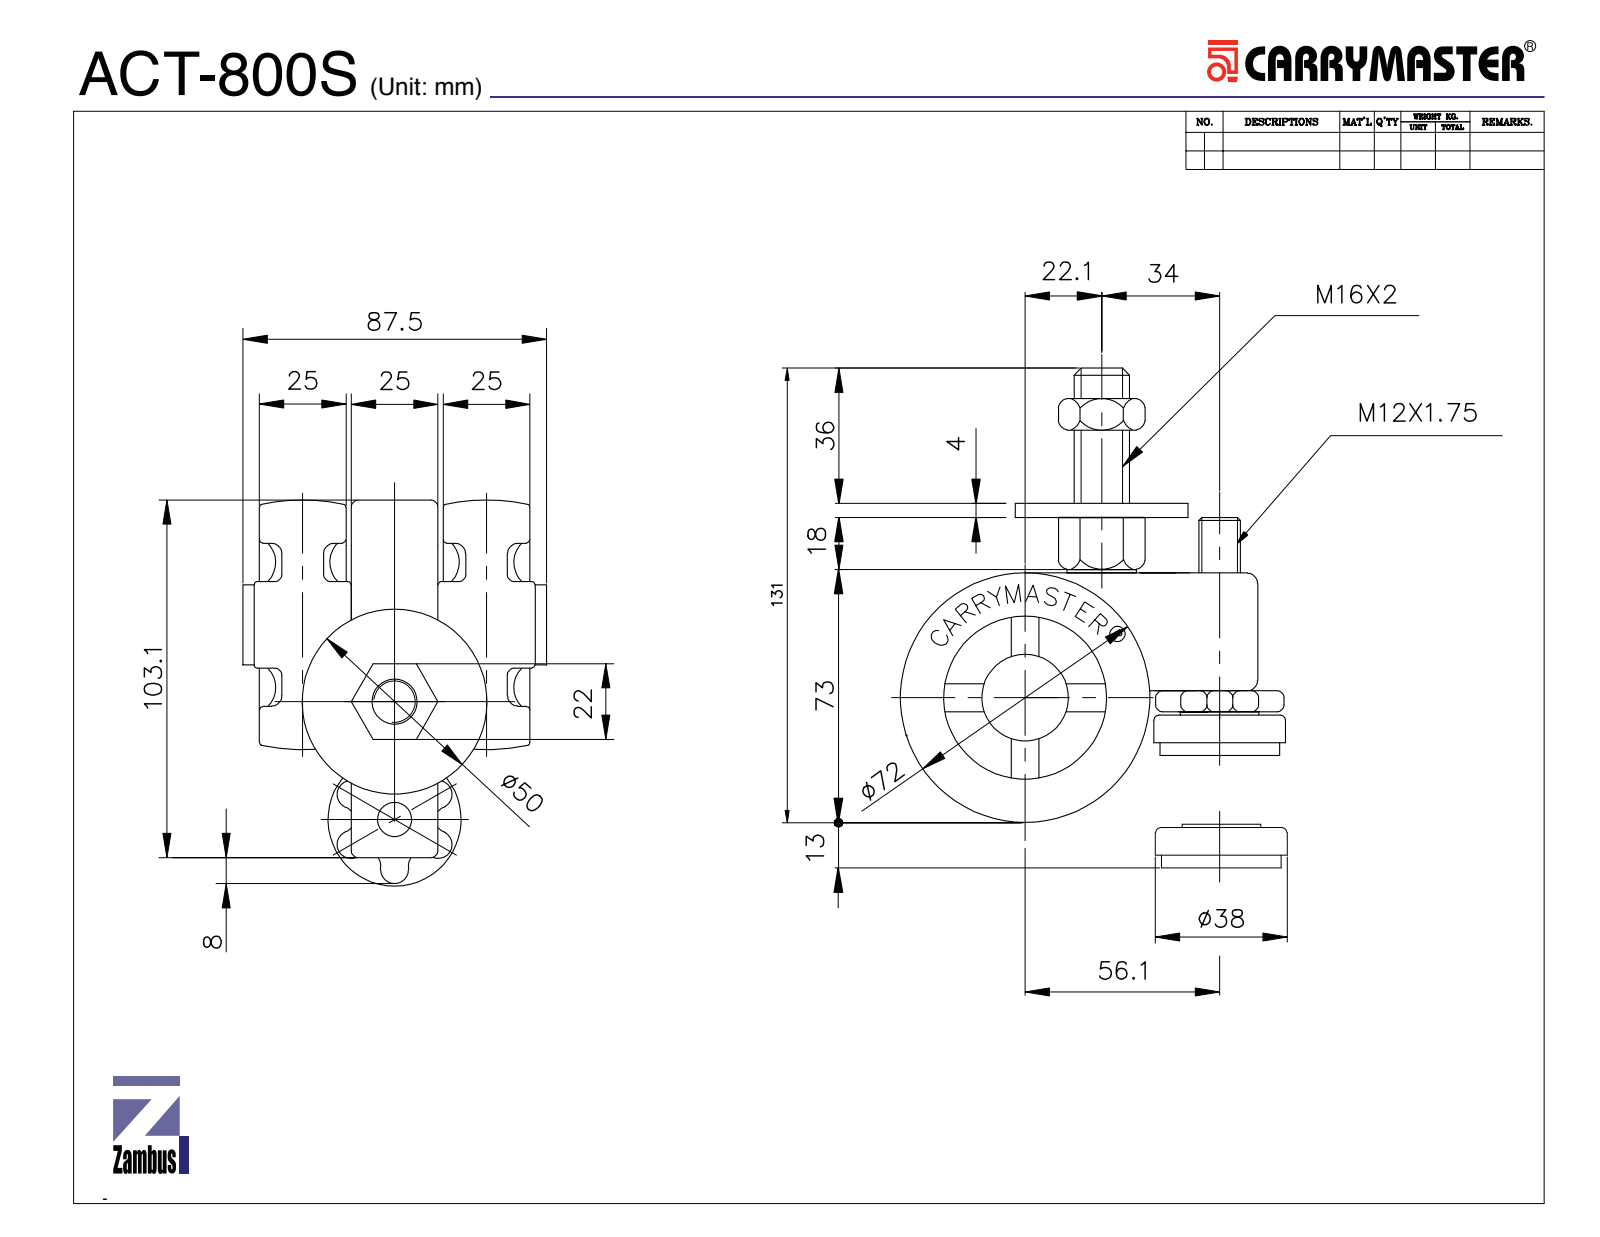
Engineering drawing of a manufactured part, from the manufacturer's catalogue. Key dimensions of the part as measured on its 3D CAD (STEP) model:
Part name (STEP PRODUCT): ACT-800S
STEP written by: SolidWorks 2015 (CONFIG_CONTROL_DESIGN)
Units: millimetres
Bodies: 12 solids, 578 faces (216 planar, 138 cylindrical, 224 other)
Overall size (bounding box): 131 × 112.25 × 85.5
Volume: 314 854 mm³ · Surface area: 79 375 mm²
Round holes (diameter × count): ⌀1.76 ×1, ⌀5 ×1, ⌀6 ×1, ⌀6.5 ×1, ⌀7.5 ×1, ⌀10 ×1, ⌀10.2 ×1, ⌀12.2 ×1, ⌀13.2 ×1, ⌀14 ×1, ⌀14.5 ×1, ⌀15 ×1
Round bosses / shafts (diameter × count): ⌀20 ×2, ⌀50 ×1, ⌀38.5 ×1, ⌀35 ×1, ⌀25 ×1, ⌀19 ×1, ⌀15.2 ×1, ⌀13 ×1
Partial cylindrical surfaces — rounded edges, fillets, slot ends (radius × count): R8 ×16, R2 ×13, R4 ×7, R4.2 ×6, R2.25 ×1, R3 ×1, R3.17 ×1, R36 ×1
Main face-to-face distances: 26.5, 25, 53, 1.5, 51.5, 28, 20, 23, 8, 6.5
Hole centre spacings: 23.9, 24.41, 35, 41.74
